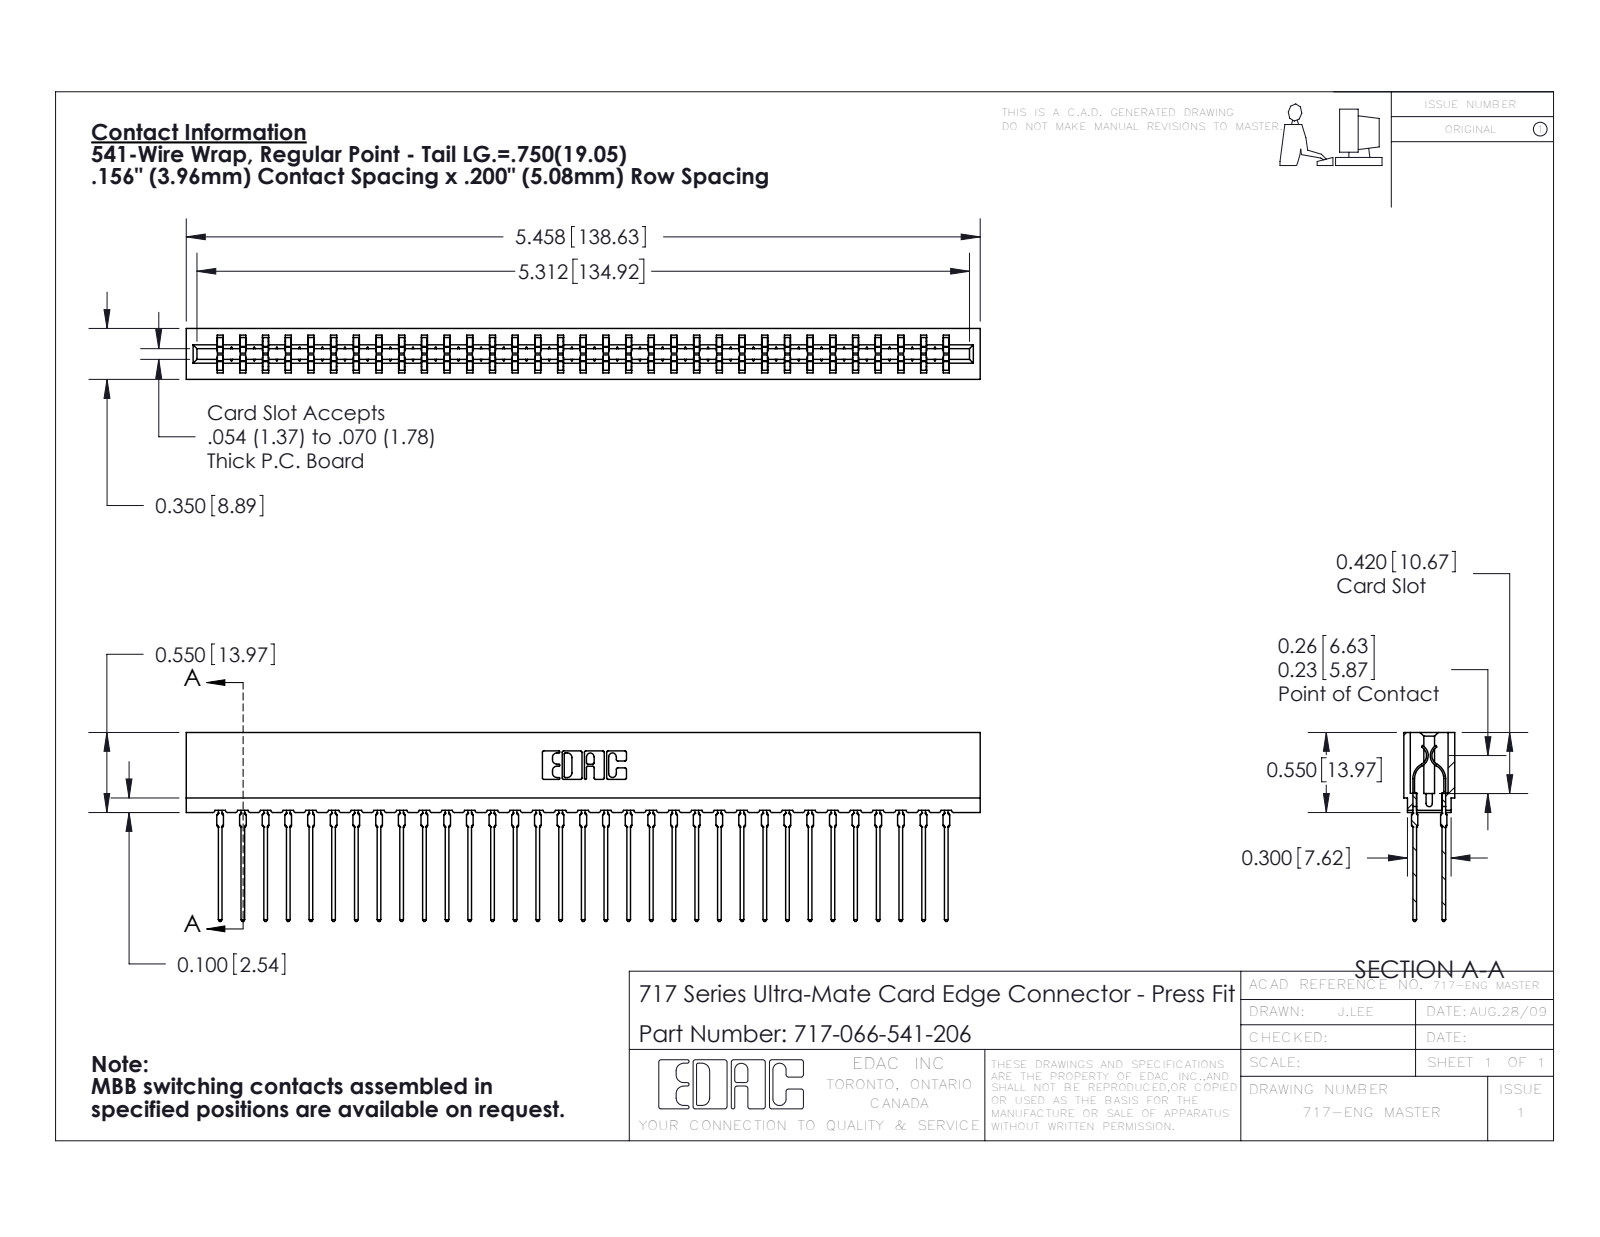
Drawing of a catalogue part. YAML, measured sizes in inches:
part_name: "717-066-541-206; 745-292-001_541; 717 Part_Insulator Option - 06"
step_written_by: "SolidWorks 2016 (CONFIG_CONTROL_DESIGN)"
units: inches
bodies: {solids: 67, faces: 6034, planar: 3123, cylindrical: 1195, other: 1716}
overall_size: [5.458, 1.299, 0.35]
volume: 0.755
surface_area: 31.43
partial_cylinders:
  - {radius: 0.021, count: 132}
  - {radius: 0.015, count: 66}
  - {radius: 0.01, count: 22}
  - {radius: 0.005, count: 8}
  - {radius: 0.011, count: 8}
  - {radius: 0.007, count: 6}
  - {radius: 0.031, count: 6}
  - {radius: 0.026, count: 3}
face_to_face_distances: [0.212, 0.138, 0.35, 0.063, 0.287, 0.076, 0.149, 0.087, 0.263, 0.025]
